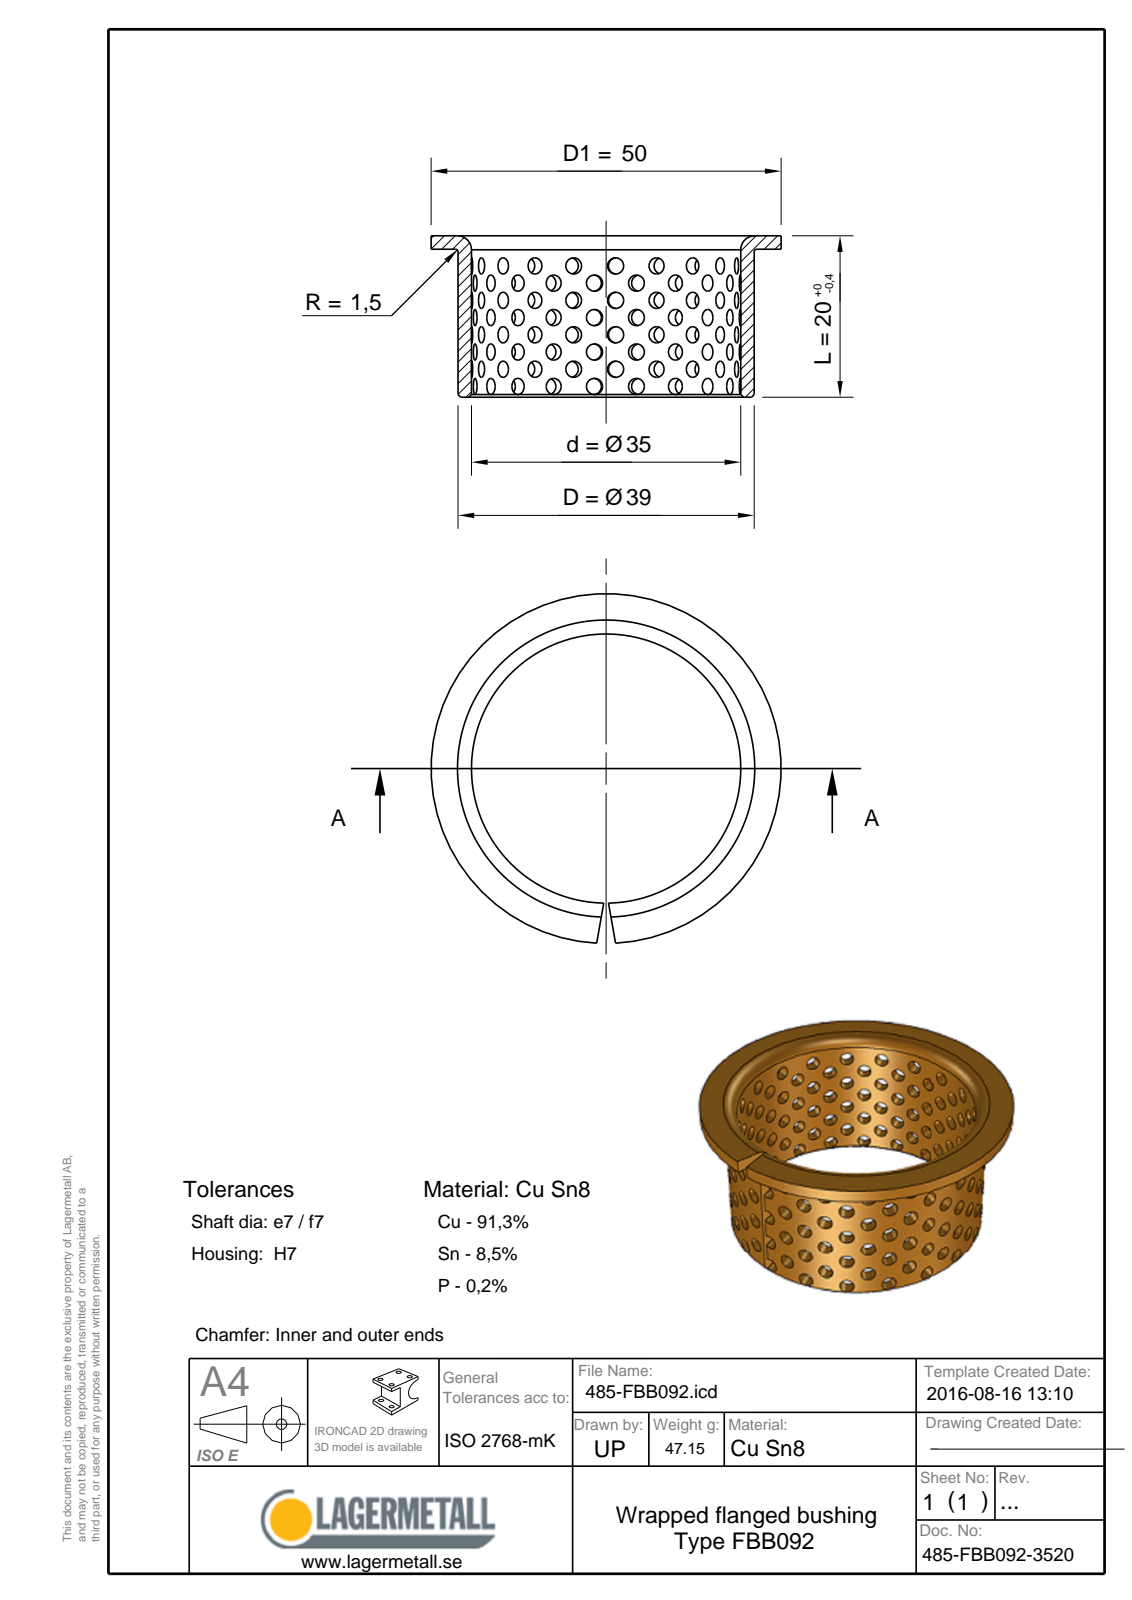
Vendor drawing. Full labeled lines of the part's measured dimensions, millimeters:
Part name (STEP PRODUCT): 485-FBB092-3520
STEP written by: Spatial InterOp 3D (CONFIG_CONTROL_DESIGN)
Units: millimetres
Bodies: 1 solid, 12 faces (5 planar, 3 cylindrical, 4 other)
Overall size (bounding box): 50 × 49.94 × 20
Volume: 5 821 mm³ · Surface area: 6 418 mm²
Round holes (diameter × count): ⌀35 ×1
Round bosses / shafts (diameter × count): ⌀50 ×1, ⌀39 ×1
Main face-to-face distances: 2, 18, 20
